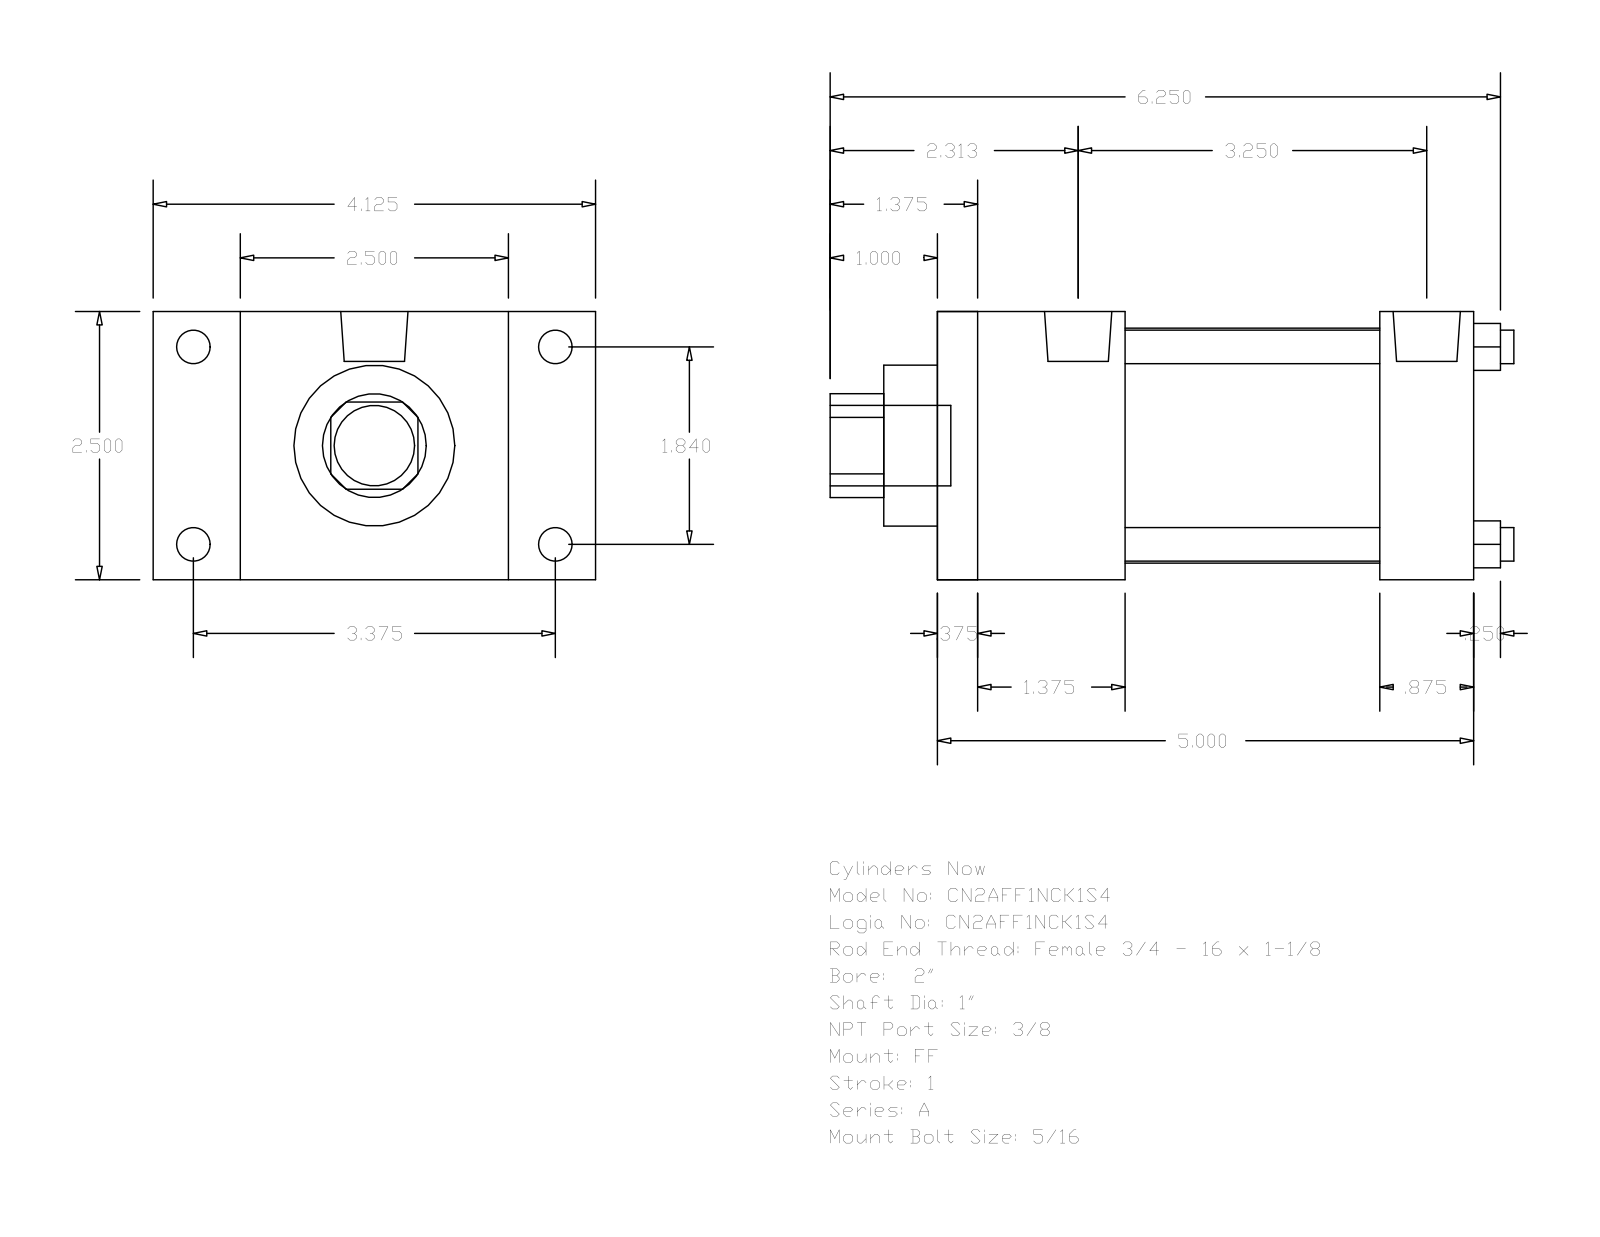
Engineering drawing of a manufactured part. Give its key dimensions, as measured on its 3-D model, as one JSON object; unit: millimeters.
{"part_name": "A_FF__0200_1", "step_written_by": "GSSL Pune (CONFIG_CONTROL_DESIGN)", "units": "millimeters", "bodies": {"solids": 0, "faces": 92, "planar": 64, "cylindrical": 28, "other": 0}, "overall_size": [161.93, 104.78, 63.5], "round_holes": [[7.94, 4], [25.4, 1], [38.1, 1], [55.63, 1]], "round_bosses_or_shafts": [[7.94, 4], [5.56, 4], [15.93, 2], [19.05, 1]], "partial_cylinders_radius": [[12.29, 1]], "face_to_face_distances": [63.5, 127, 117.48, 9.52, 22.22, 104.78, 20.64, 44.45, 34.93, 95.26], "hole_center_spacings": [33.05, 46.74, 66.1]}
